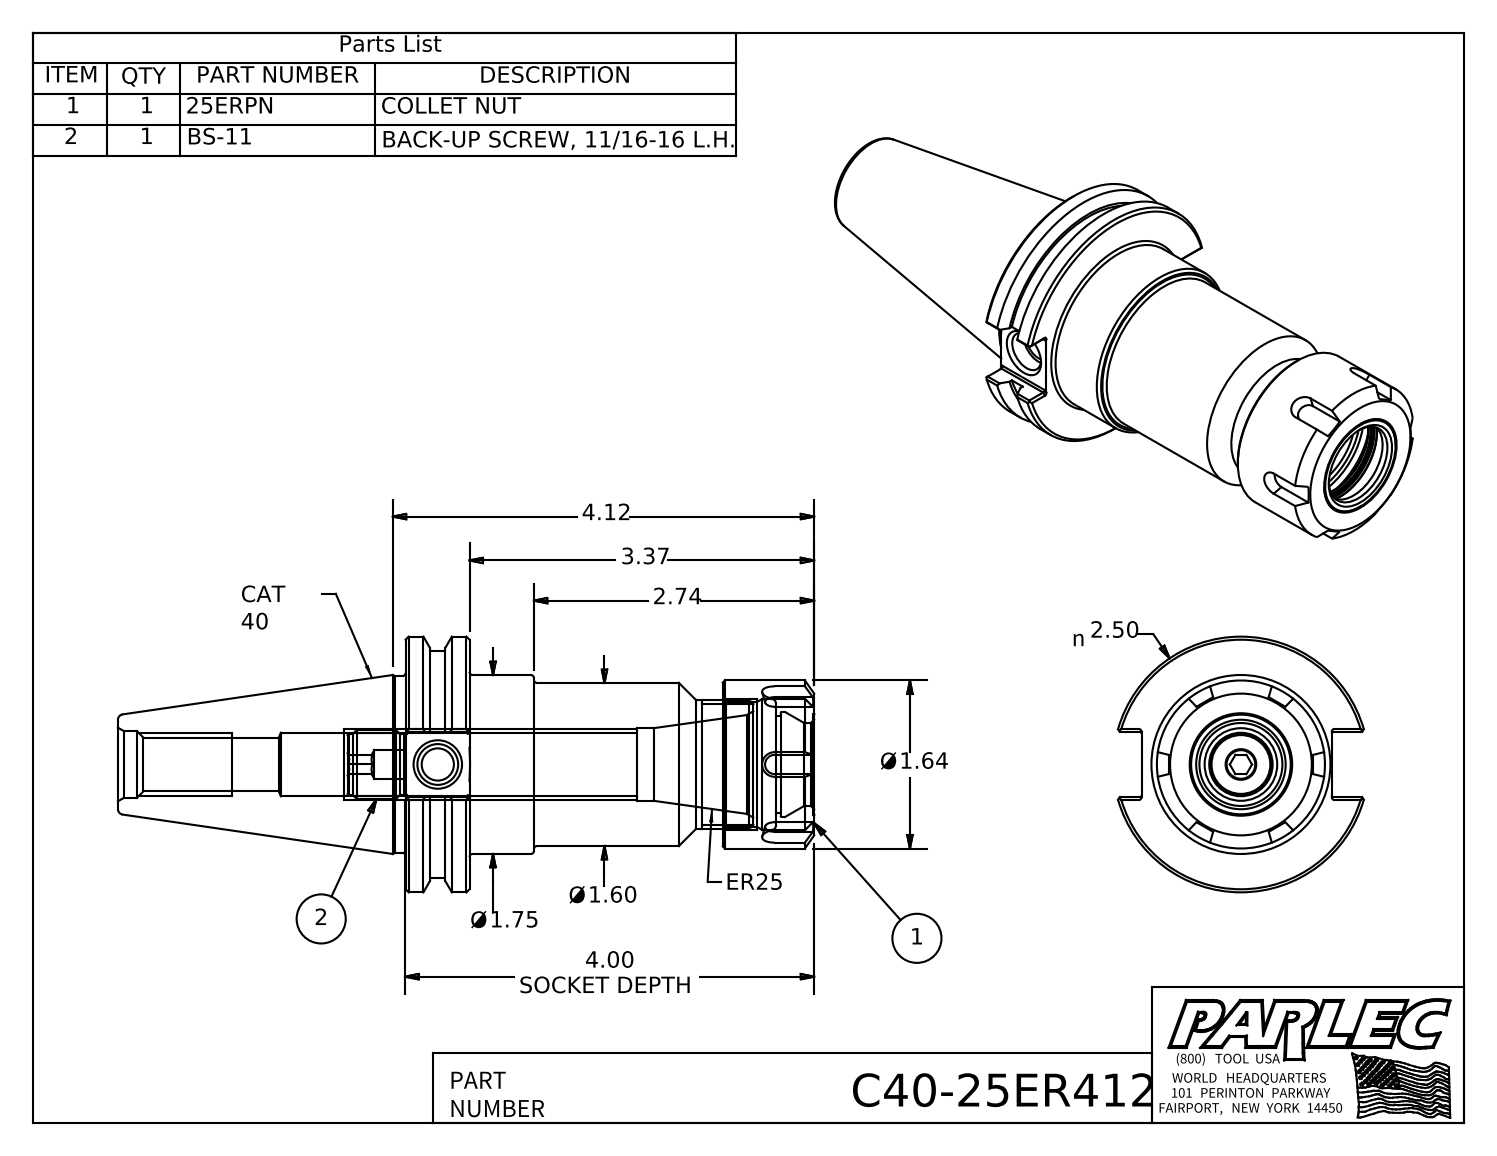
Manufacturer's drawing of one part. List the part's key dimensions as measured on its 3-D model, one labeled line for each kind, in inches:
Part name (STEP PRODUCT): C40-25ER412; C40-25ER4-1; 25ERPN; BS-11
STEP written by: Autodesk Inventor 2012 (AUTOMOTIVE_DESIGN)
Units: inches
Bodies: 3 solids, 152 faces (64 planar, 38 cylindrical, 50 other)
Overall size (bounding box): 6.808 × 2.5 × 2.403
Volume: 11.26 in³ · Surface area: 63.38 in²
Round holes (diameter × count): ⌀0.28 ×1, ⌀0.315 ×1, ⌀0.399 ×1, ⌀0.527 ×1, ⌀0.62 ×1, ⌀0.648 ×1, ⌀0.71 ×1, ⌀0.811 ×1, ⌀0.95 ×1, ⌀1.027 ×1, ⌀1.217 ×1, ⌀1.28 ×1
Round bosses / shafts (diameter × count): ⌀2.5 ×1, ⌀2.219 ×1, ⌀1.75 ×1, ⌀1.73 ×1, ⌀1.643 ×1, ⌀1.595 ×1, ⌀1.26 ×1, ⌀0.681 ×1
Partial cylindrical surfaces — rounded edges, fillets, slot ends (radius × count): R0.02 ×12
Main face-to-face distances: 0.625, 3.995, 3.37, 3.102, 2.477, 0.893, 3.62, 2.995, 0.518, 0.375
